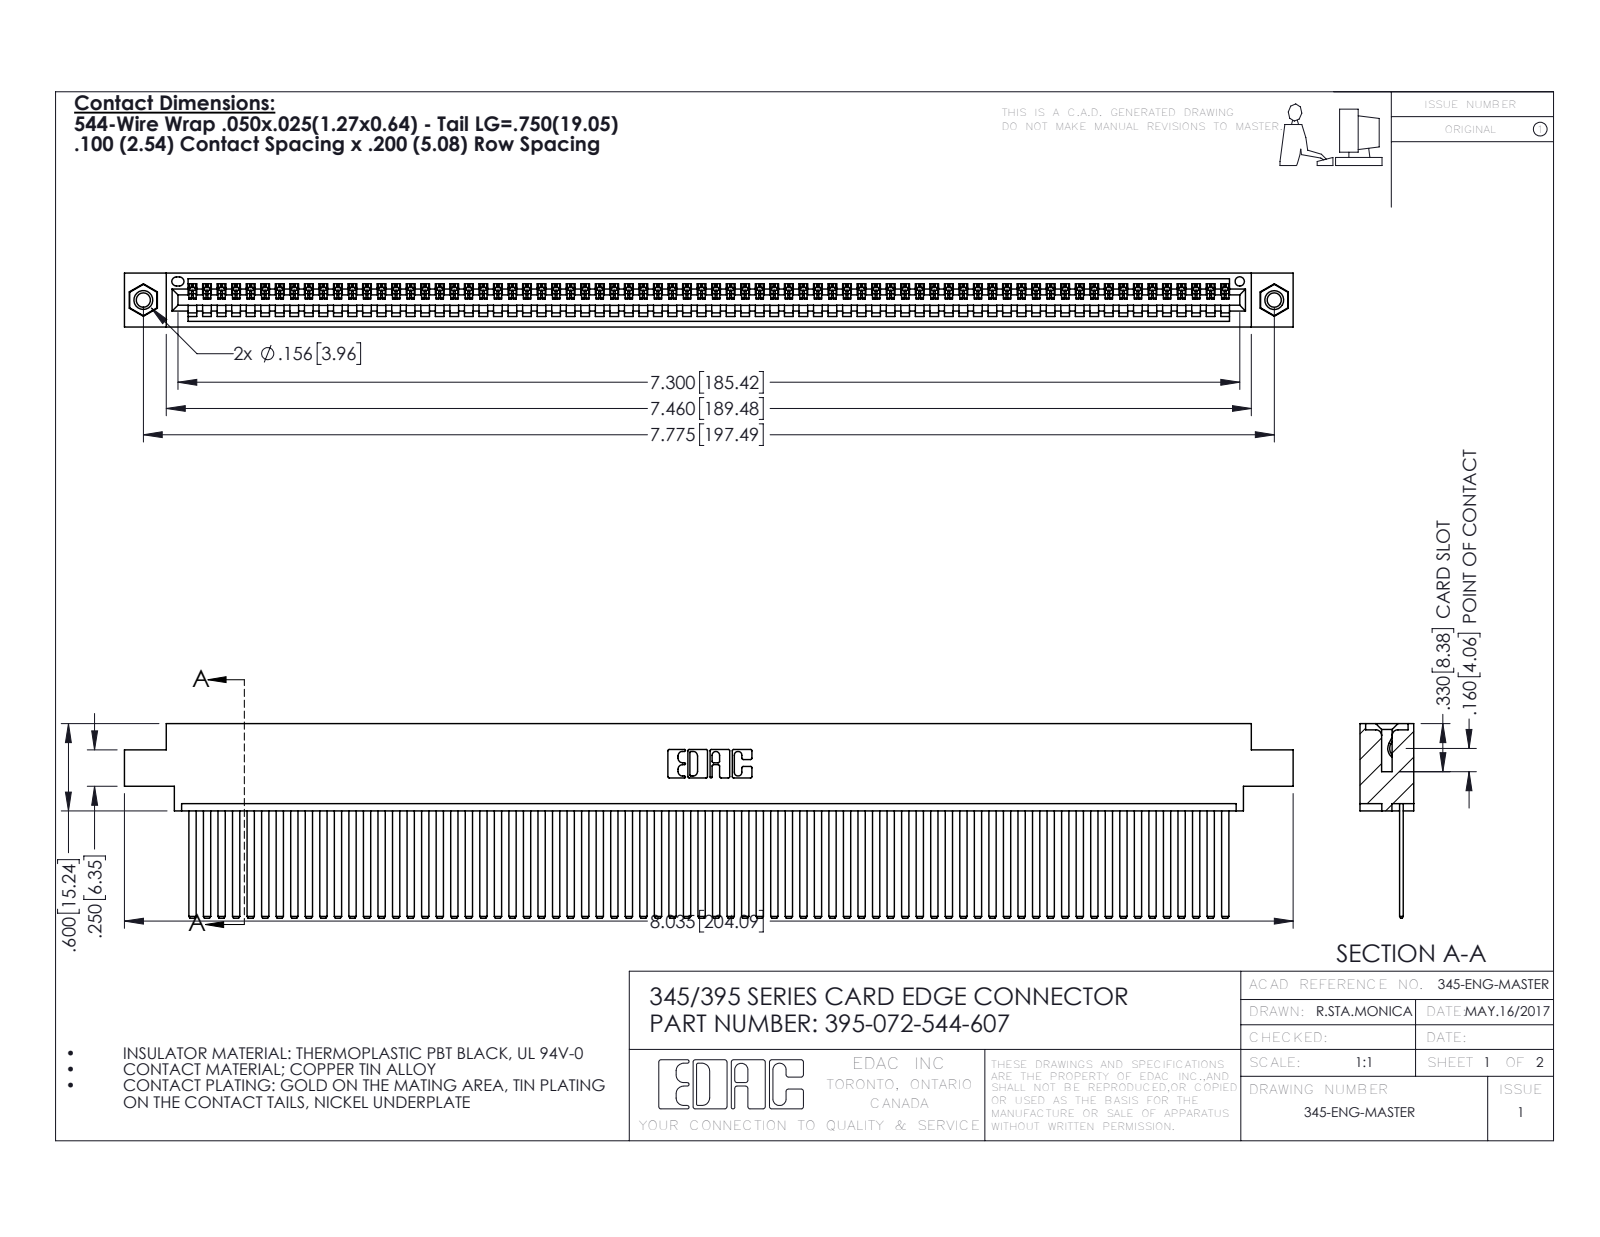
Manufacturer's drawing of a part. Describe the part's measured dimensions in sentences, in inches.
The part is named "345-250-001_345-250-005-103; 345 Part_0.170 Offset - 0.156 Dia-TI; 395-072-544-607; 345-292-001_345-293-144". Its 3-D file was written by "SolidWorks 2016 (CONFIG_CONTROL_DESIGN)". It is 75 solids with 3934 faces: 2708 planar, 1210 cylindrical and 16 other. Overall it measures 8.035 by 1.337 by 0.37 inches. Its volume is 1.241 cubic inches and its surface area 46.65 square inches. Round holes: 2 of diameter 0.098, 2 of diameter 0.125, 2 of diameter 0.156, 1 of diameter 0.064. Round bosses or shafts: 2 of diameter 0.155. Partial cylindrical surfaces (rounded edges, fillets, slot ends): 144 of radius 0.006, 22 of radius 0.01, 6 of radius 0.007, 6 of radius 0.031, 3 of radius 0.026, 2 of radius 0.031, 2 of radius 0.04, 1 of radius 0.014. The main face-to-face distances are 0.072, 0.298, 0.025, 0.098, 0.272, 0.37, 0.2, 0.225, 0.149, 0.175. The hole center spacings are 0.27, 7.539, 7.775.
